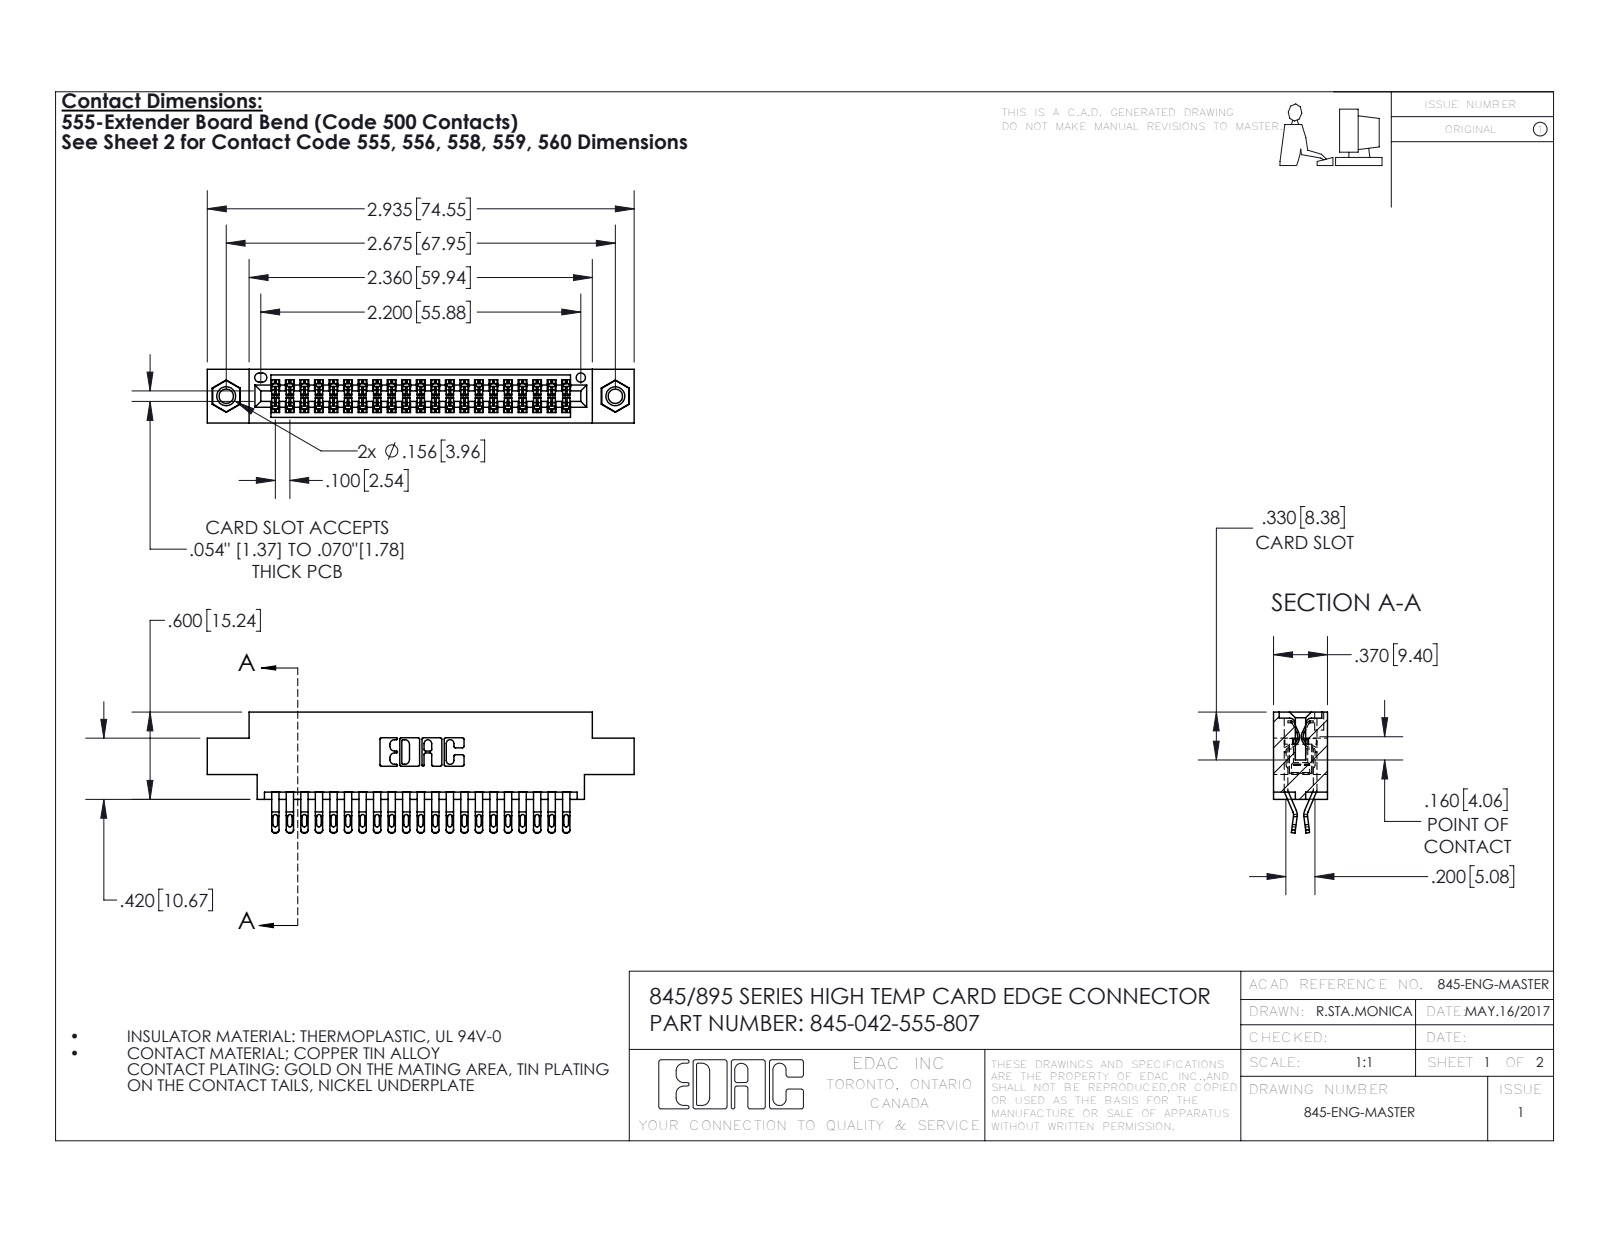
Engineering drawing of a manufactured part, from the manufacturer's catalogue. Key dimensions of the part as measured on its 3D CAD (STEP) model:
Part name (STEP PRODUCT): 345-042-555-807; 345 Part_0.170 Offset - 0.156 Dia-TI; 345-250-001_345-250-005-103; 345-292-001_555 Tail
STEP written by: SolidWorks 2016 (CONFIG_CONTROL_DESIGN)
Units: inches
Bodies: 45 solids, 2542 faces (1418 planar, 1108 cylindrical, 16 other)
Overall size (bounding box): 2.935 × 0.832 × 0.37
Volume: 0.43 in³ · Surface area: 16.43 in²
Round holes (diameter × count): ⌀0.098 ×2, ⌀0.125 ×2, ⌀0.156 ×2, ⌀0.064 ×1
Round bosses / shafts (diameter × count): ⌀0.155 ×2
Partial cylindrical surfaces — rounded edges, fillets, slot ends (radius × count): R0.016 ×105, R0.02 ×84, R0.006 ×63, R0.01 ×22, R0.007 ×6, R0.031 ×6, R0.026 ×3, R0.01 ×2
Main face-to-face distances: 0.072, 0.298, 0.37, 0.2, 0.025, 0.098, 0.272, 0.225, 0.175, 0.149
Hole centre spacings: 0.27, 2.441, 2.675
